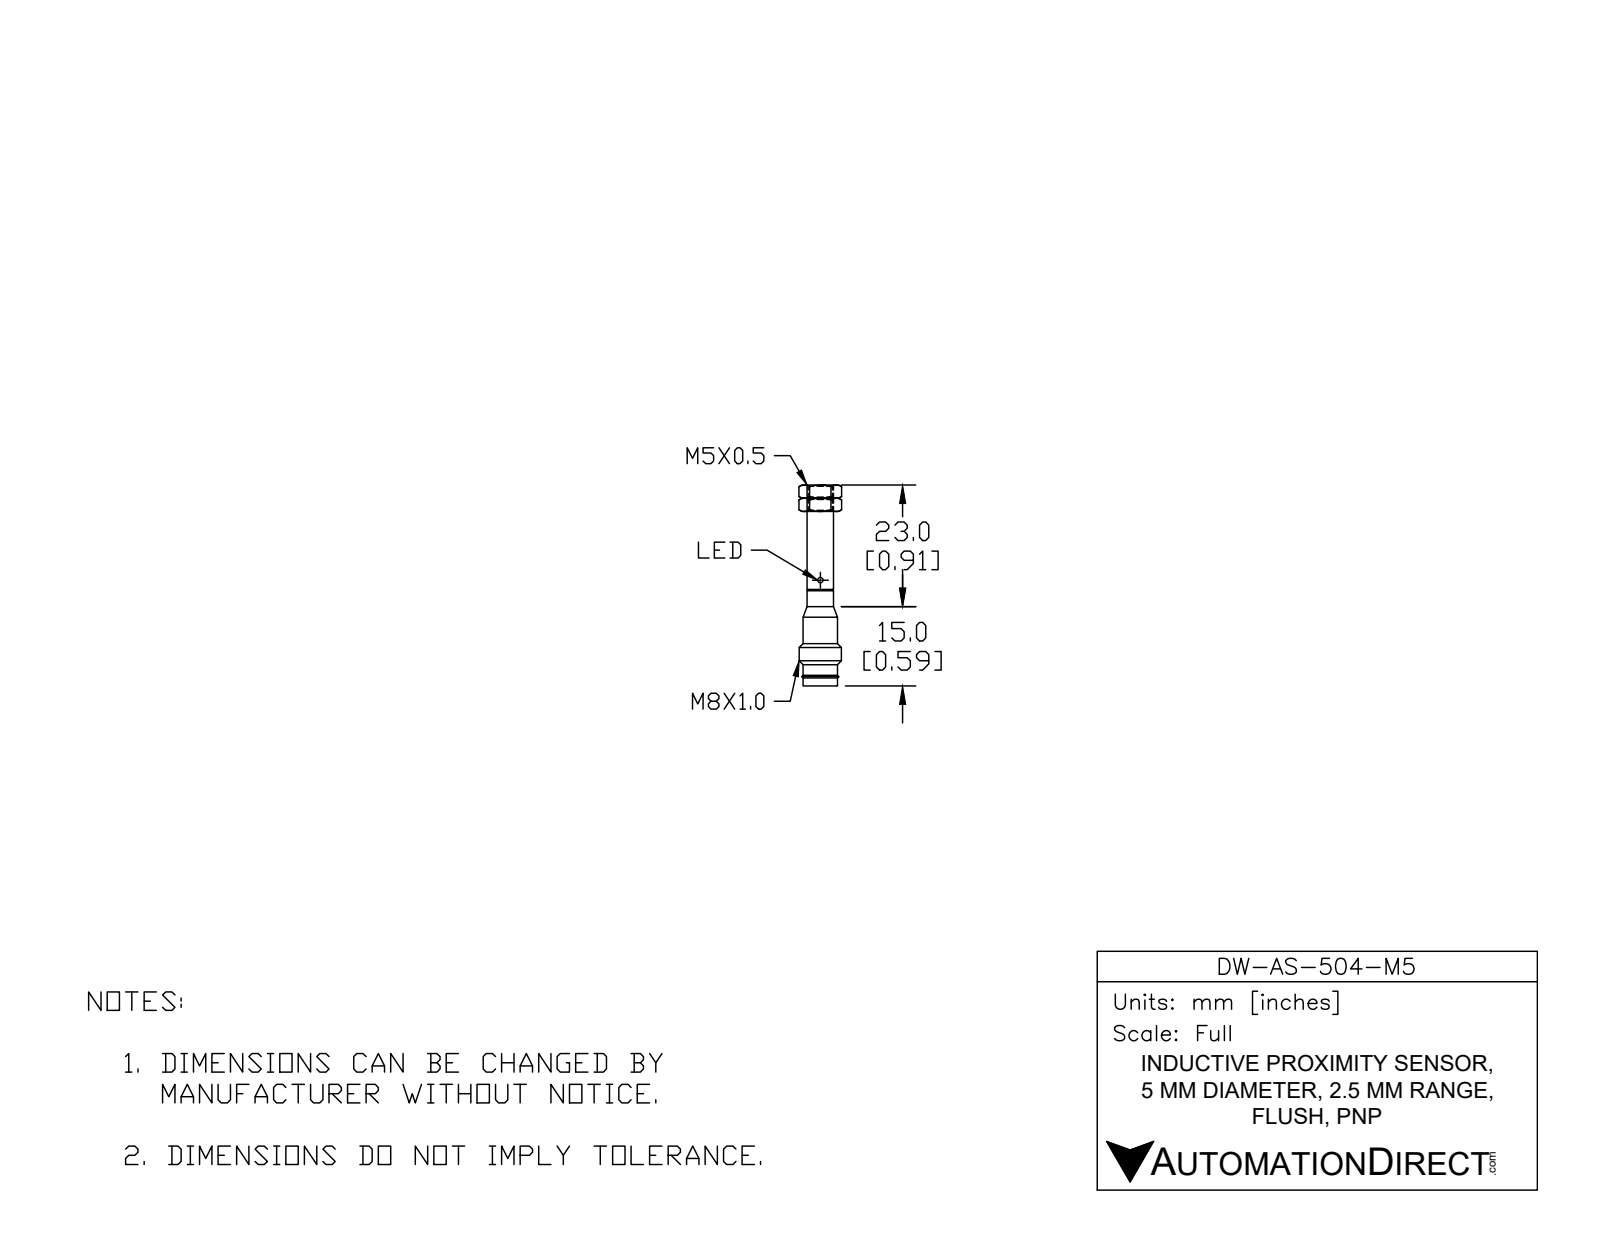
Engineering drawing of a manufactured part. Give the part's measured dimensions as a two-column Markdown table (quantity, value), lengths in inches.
| quantity | value |
| --- | --- |
| part name | DW-AS-504-M5 |
| STEP written by | SolidWorks 2017 (AUTOMOTIVE_DESIGN) |
| units | inches |
| bodies | 4 solids, 42 faces (11 planar, 15 cylindrical, 16 other) |
| overall size | 1.496 × 0.315 × 0.315 |
| volume | 0.026 in³ |
| surface area | 2.173 in² |
| round holes (diameter × count) | 0.059 × 1, 0.14 × 1, 0.217 × 1, 0.228 × 1 |
| round bosses / shafts (diameter × count) | 0.039 × 3, 0.315 × 1, 0.272 × 1, 0.256 × 1, 0.228 × 1, 0.197 × 1, 0.132 × 1 |
| main face-to-face distances | 0.03, 1.269, 1.299, 1.267, 1.297, 0.051, 0.049, 1.218, 1.248, 0.047 |
